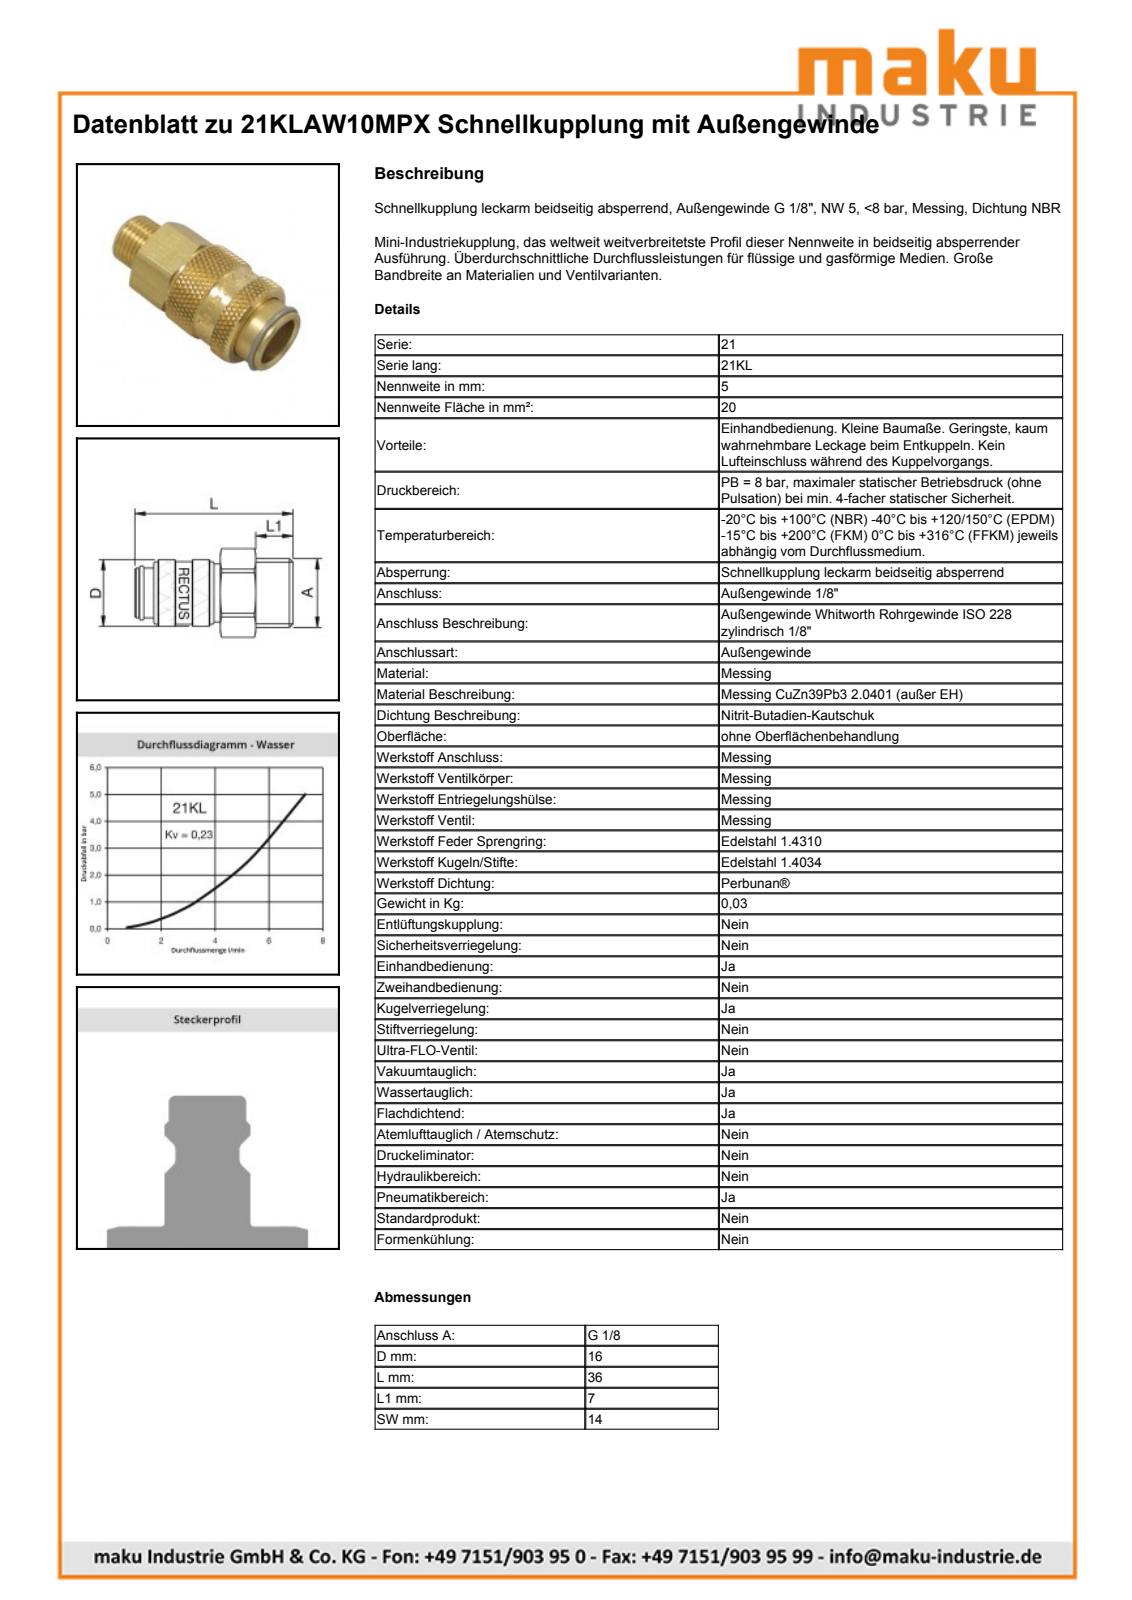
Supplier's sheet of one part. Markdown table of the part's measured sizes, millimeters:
| quantity | value |
| --- | --- |
| part name | D106530 |
| STEP written by | Autodesk Inventor 2013 (AUTOMOTIVE_DESIGN) |
| units | millimeters |
| bodies | 2 solids, 340 faces (122 planar, 46 cylindrical, 172 other) |
| overall size | 36 × 16 × 16 |
| volume | 5 107 mm³ |
| surface area | 3 368 mm² |
| round holes (diameter × count) | 12.15 × 1, 12.75 × 1, 14 × 1, 14.6 × 1 |
| round bosses / shafts (diameter × count) | 16 × 1, 15 × 1, 12 × 1, 11.15 × 1, 9.73 × 1 |
| partial cylindrical surfaces (radius × count) | 7.4 × 1, 7.9 × 1 |
| main face-to-face distances | 14, 29, 4.5, 24.5, 36, 31.5, 7, 16, 11.5, 13 |
